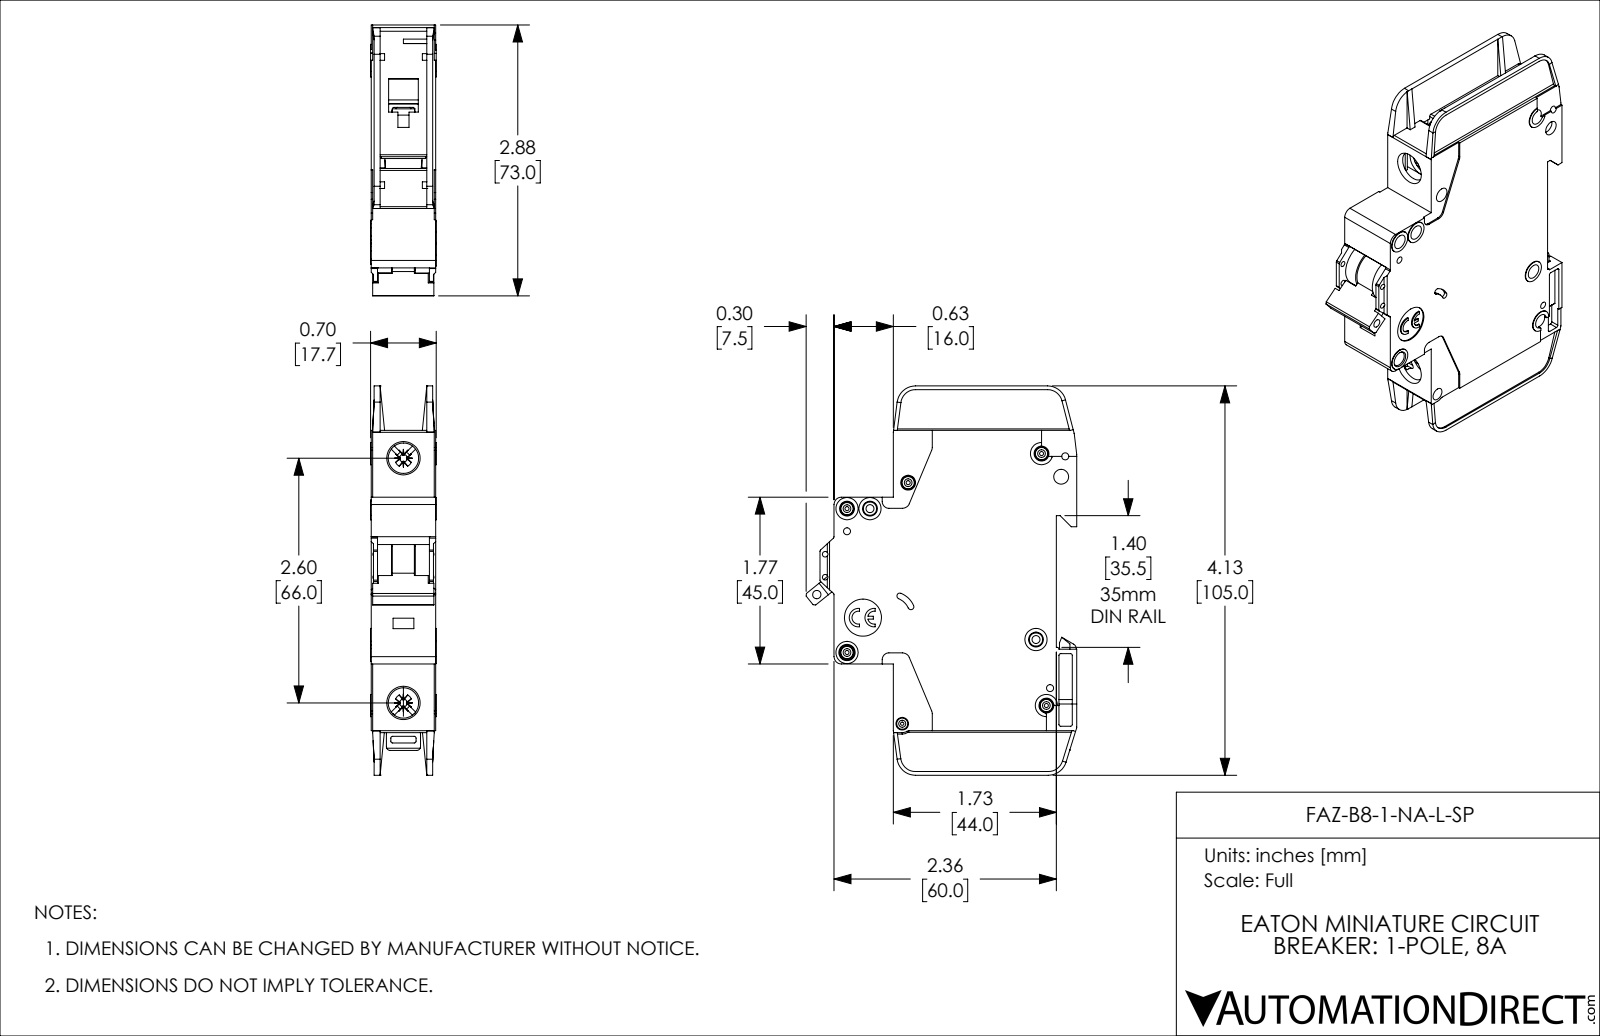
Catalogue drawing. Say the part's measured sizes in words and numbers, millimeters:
The part is named "FAZ-B8-1-NA-L-SP". Its 3-D file was written by "SolidWorks 2019 (AUTOMOTIVE_DESIGN)". It is 1 solid with 1127 faces: 671 planar, 357 cylindrical and 99 other. Overall it measures 105 by 73.1 by 17.7 millimeters. Its volume is 76 720 cubic millimeters and its surface area 26 460 square millimeters. Round holes: 8 of diameter 4, 5 of diameter 1.1, 4 of diameter 1.9, 2 of diameter 1.5, 2 of diameter 2.2, 2 of diameter 8.2, 1 of diameter 0.9, 1 of diameter 2.3, 1 of diameter 2.5, 1 of diameter 3.4, 1 of diameter 10. Round bosses or shafts: 5 of diameter 3.3, 4 of diameter 6, 2 of diameter 3, 1 of diameter 2.5. Partial cylindrical surfaces (rounded edges, fillets, slot ends): 42 of radius 0.5, 10 of radius 0.4, 10 of radius 1, 8 of radius 2, 5 of radius 5, 4 of radius 0.2, 4 of radius 0.7, 4 of radius 1.1. The main face-to-face distances are 1.2, 17.4, 15, 16.2, 2.4, 13.8, 0.4, 0.8, 12.6, 14.6. The hole center spacings are 6.2, 13.6, 22.1, 4.8, 5.1, 5.2, 5.6, 6.1.
